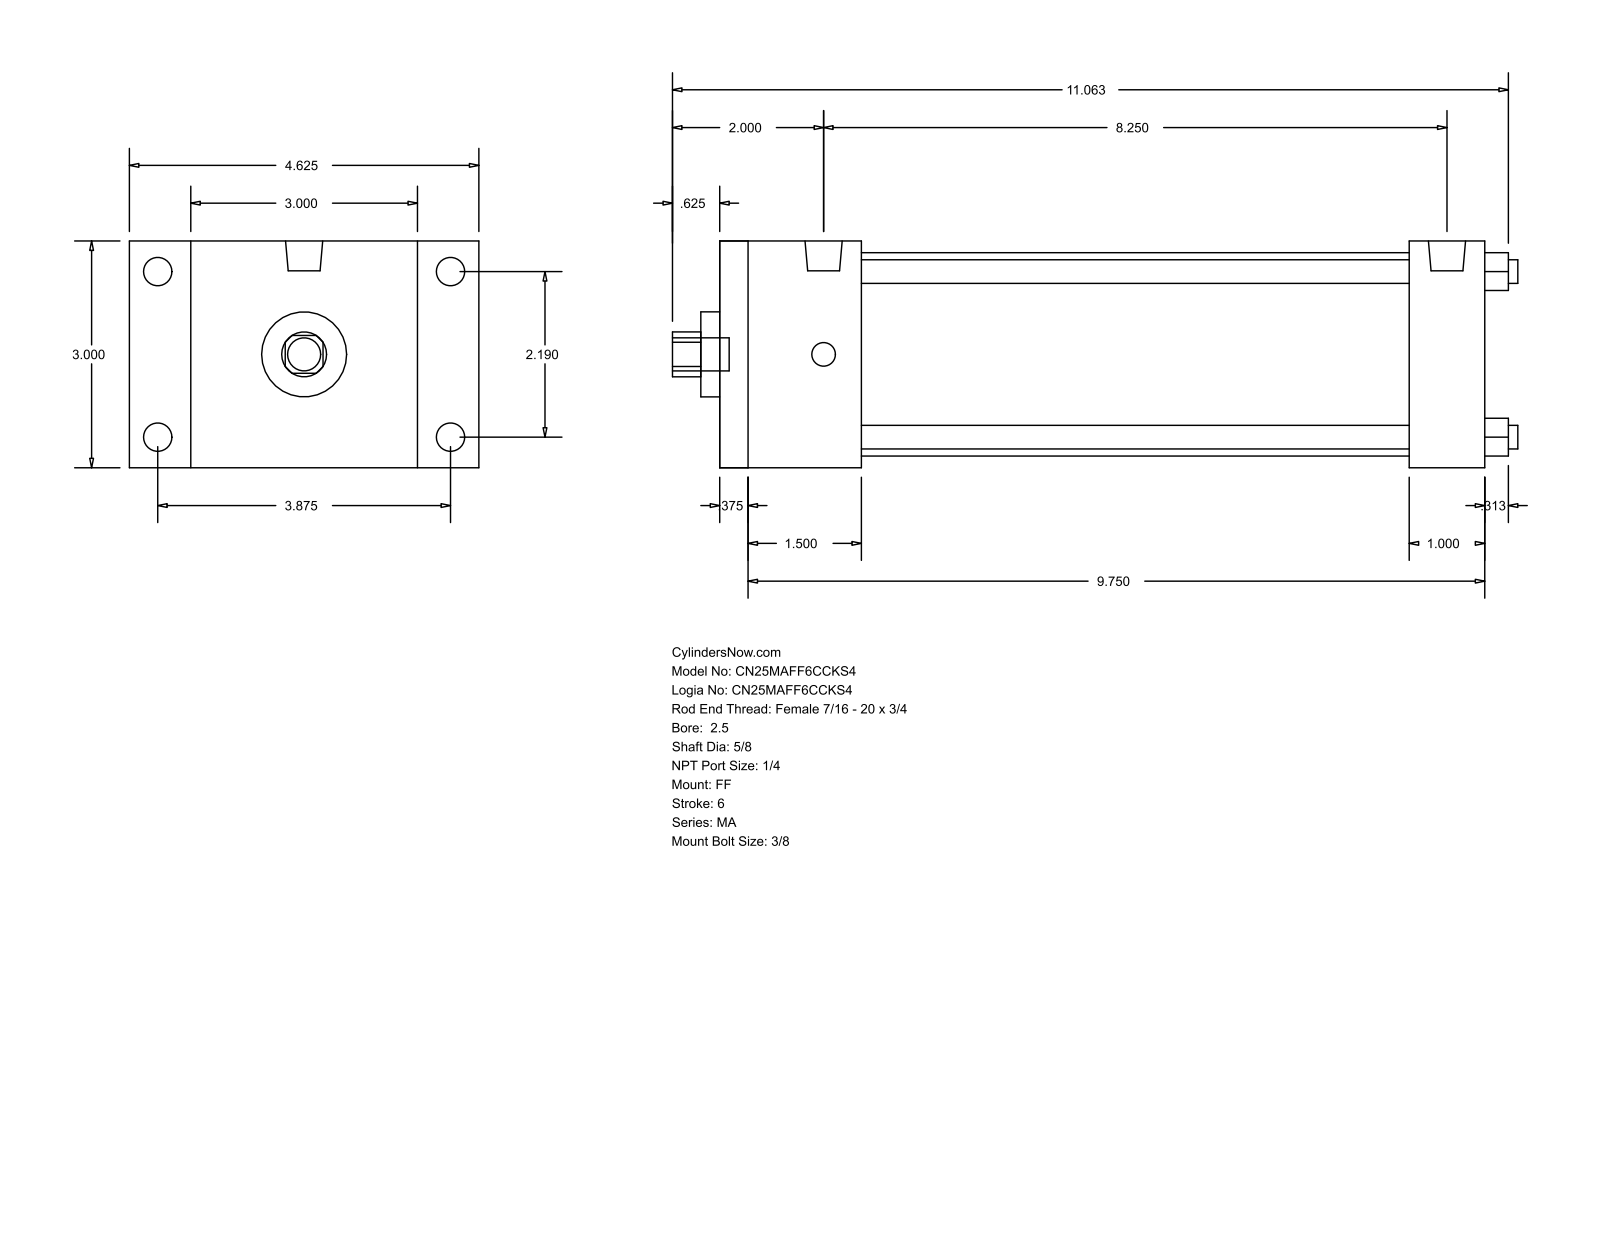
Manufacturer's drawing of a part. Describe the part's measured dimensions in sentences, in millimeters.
The part is named "MA_FF__0250_0.625". Its 3-D file was written by "GSSL Pune (CONFIG_CONTROL_DESIGN)". It is 0 solids with 92 faces: 64 planar, 28 cylindrical and 0 other. Overall it measures 284.16 by 117.47 by 76.2 millimeters. Round holes: 4 of diameter 7.94, 1 of diameter 15.88, 1 of diameter 28.57, 1 of diameter 68.33. Round bosses or shafts: 4 of diameter 9.53, 4 of diameter 7.94, 2 of diameter 12.49, 1 of diameter 11.11. Partial cylindrical surfaces (rounded edges, fillets, slot ends): 1 of radius 7.54. The main face-to-face distances are 76.2, 257.17, 9.52, 247.65, 25.4, 47.62, 231.77, 38.1, 222.25, 184.15. The hole center spacings are 39.33, 55.62, 78.66.
